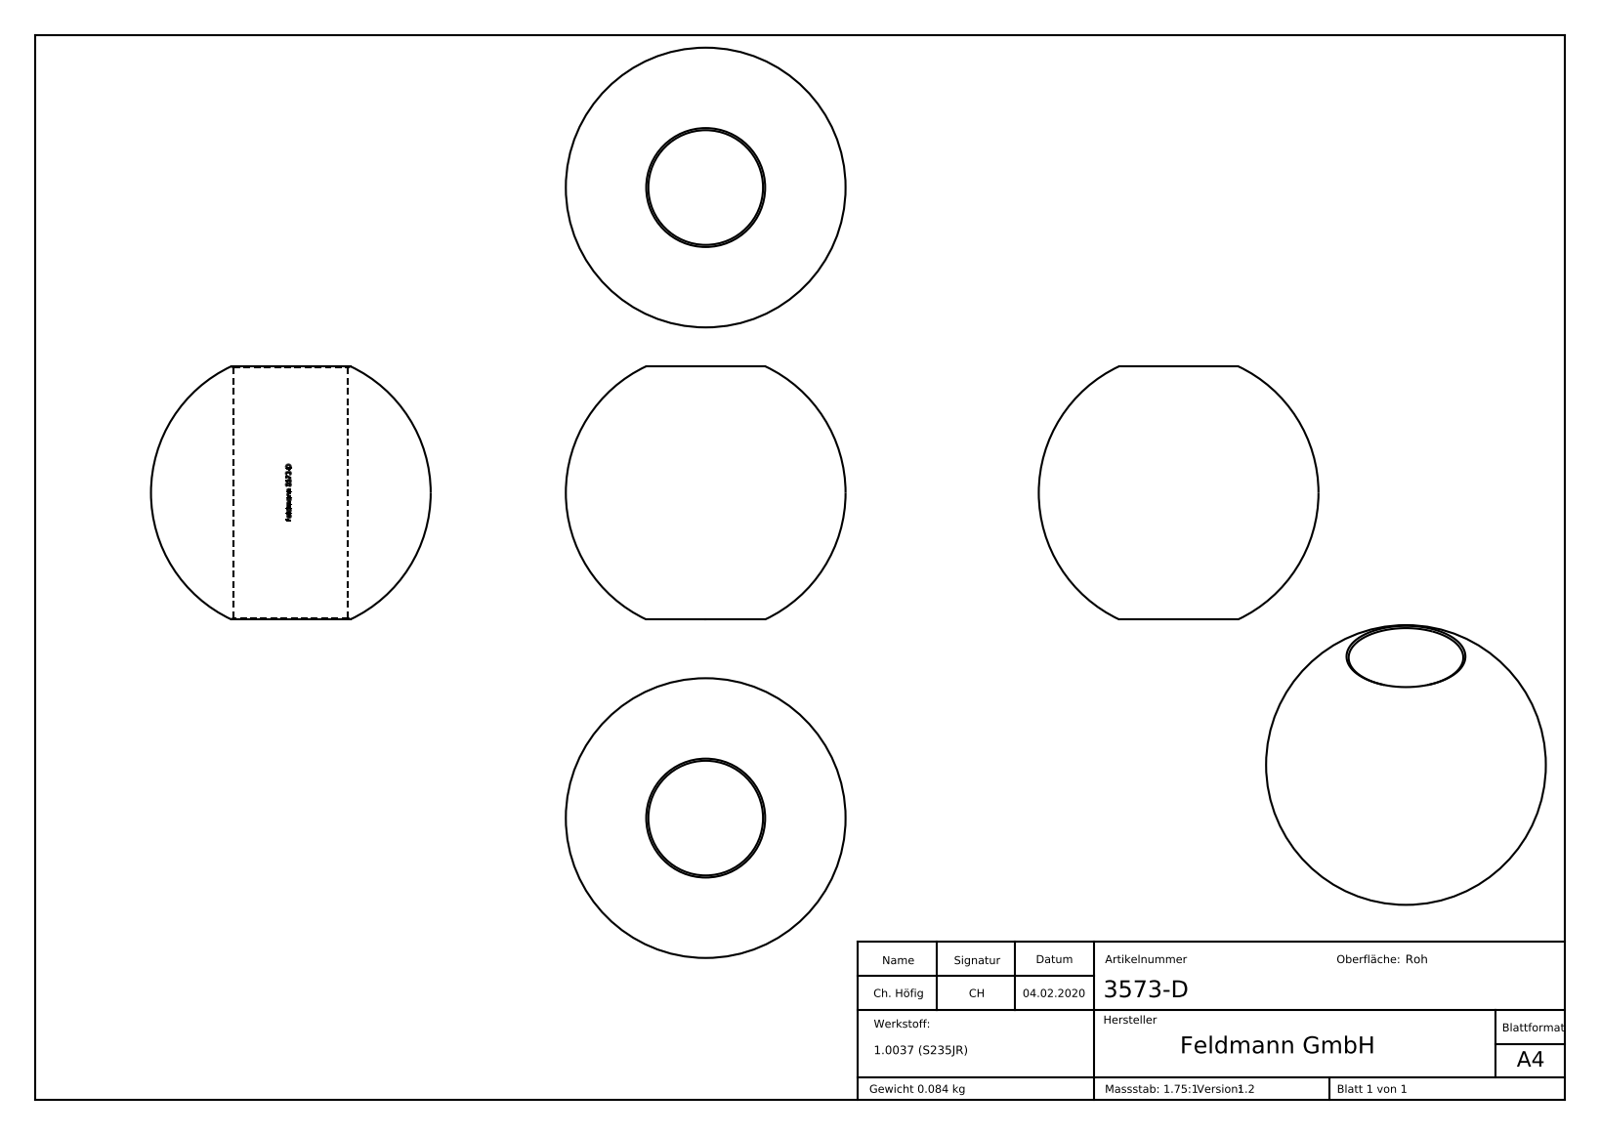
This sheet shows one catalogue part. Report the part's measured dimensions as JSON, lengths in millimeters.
{"part_name": "3573-D", "step_written_by": "SolidWorks 2015 (CONFIG_CONTROL_DESIGN)", "units": "millimeters", "bodies": {"solids": 1, "faces": 195, "planar": 82, "cylindrical": 19, "other": 94}, "overall_size": [30, 30, 27.16], "volume_mm3": 10724, "surface_area_mm2": 3622, "round_holes": [[12.3, 1]], "partial_cylinders_radius": [[6.25, 1]], "face_to_face_distances": [1.19, 0.53, 0.66, 0.45, 3.1, 0.5, 0.8, 1.3, 0.61, 1.64]}
